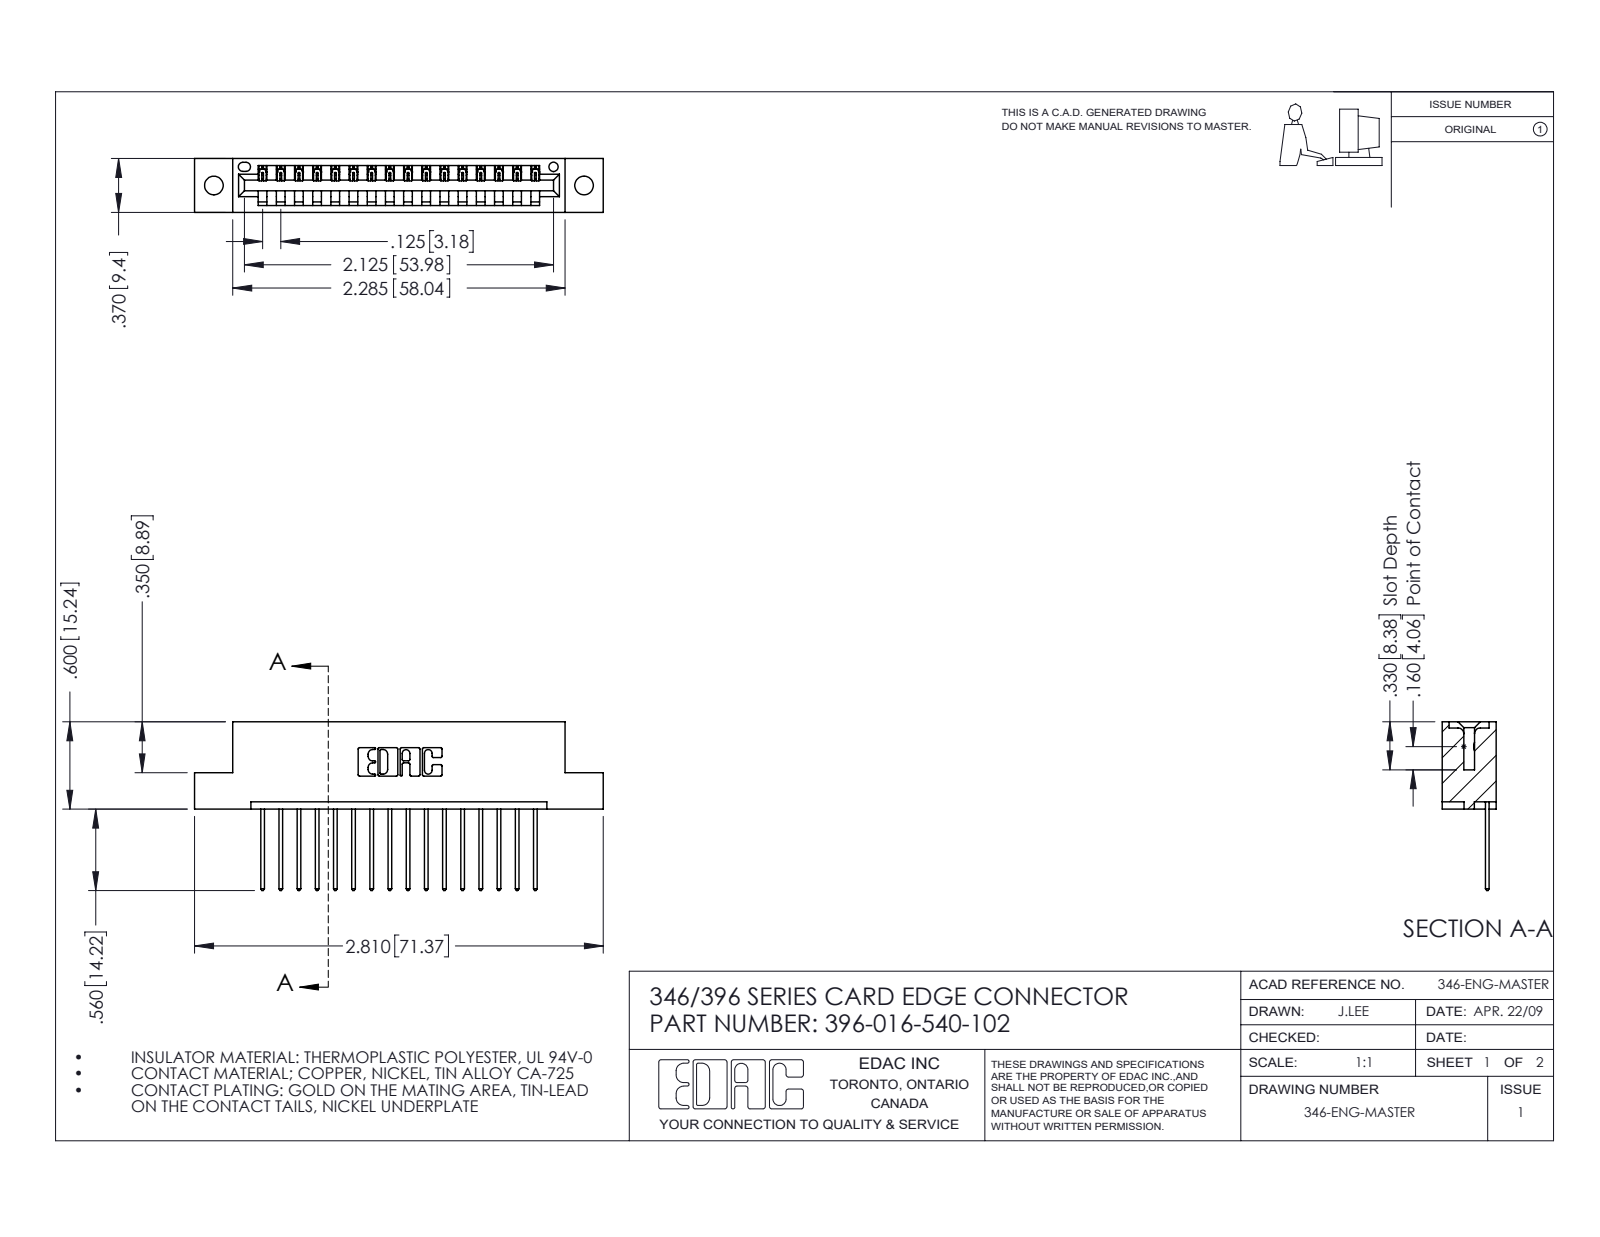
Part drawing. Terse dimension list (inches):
name: 396-016-540-102; 346 Part_Flush Mounting Lugs - 0.128 Dia; 345-292-001_345-293-140
written by: SolidWorks 2016 (CONFIG_CONTROL_DESIGN)
unit: in
bodies: 17 solids, 1050 faces (716 planar, 334 cylindrical, 0 other)
size: 2.81 × 1.16 × 0.37
volume: 0.405 in³; area: 12.25 in²
holes: 2× ⌀0.128, 1× ⌀0.064
rounds: 32× R0.006, 32× R0.01, 22× R0.01, 6× R0.007, 6× R0.031, 3× R0.026, 2× R0.031, 2× R0.04
face distances: 0.048, 0.322, 0.25, 0.37, 0.072, 0.298, 0.025, 0.148, 0.222, 0.1
hole spacings: 0.246, 2.338, 2.545
